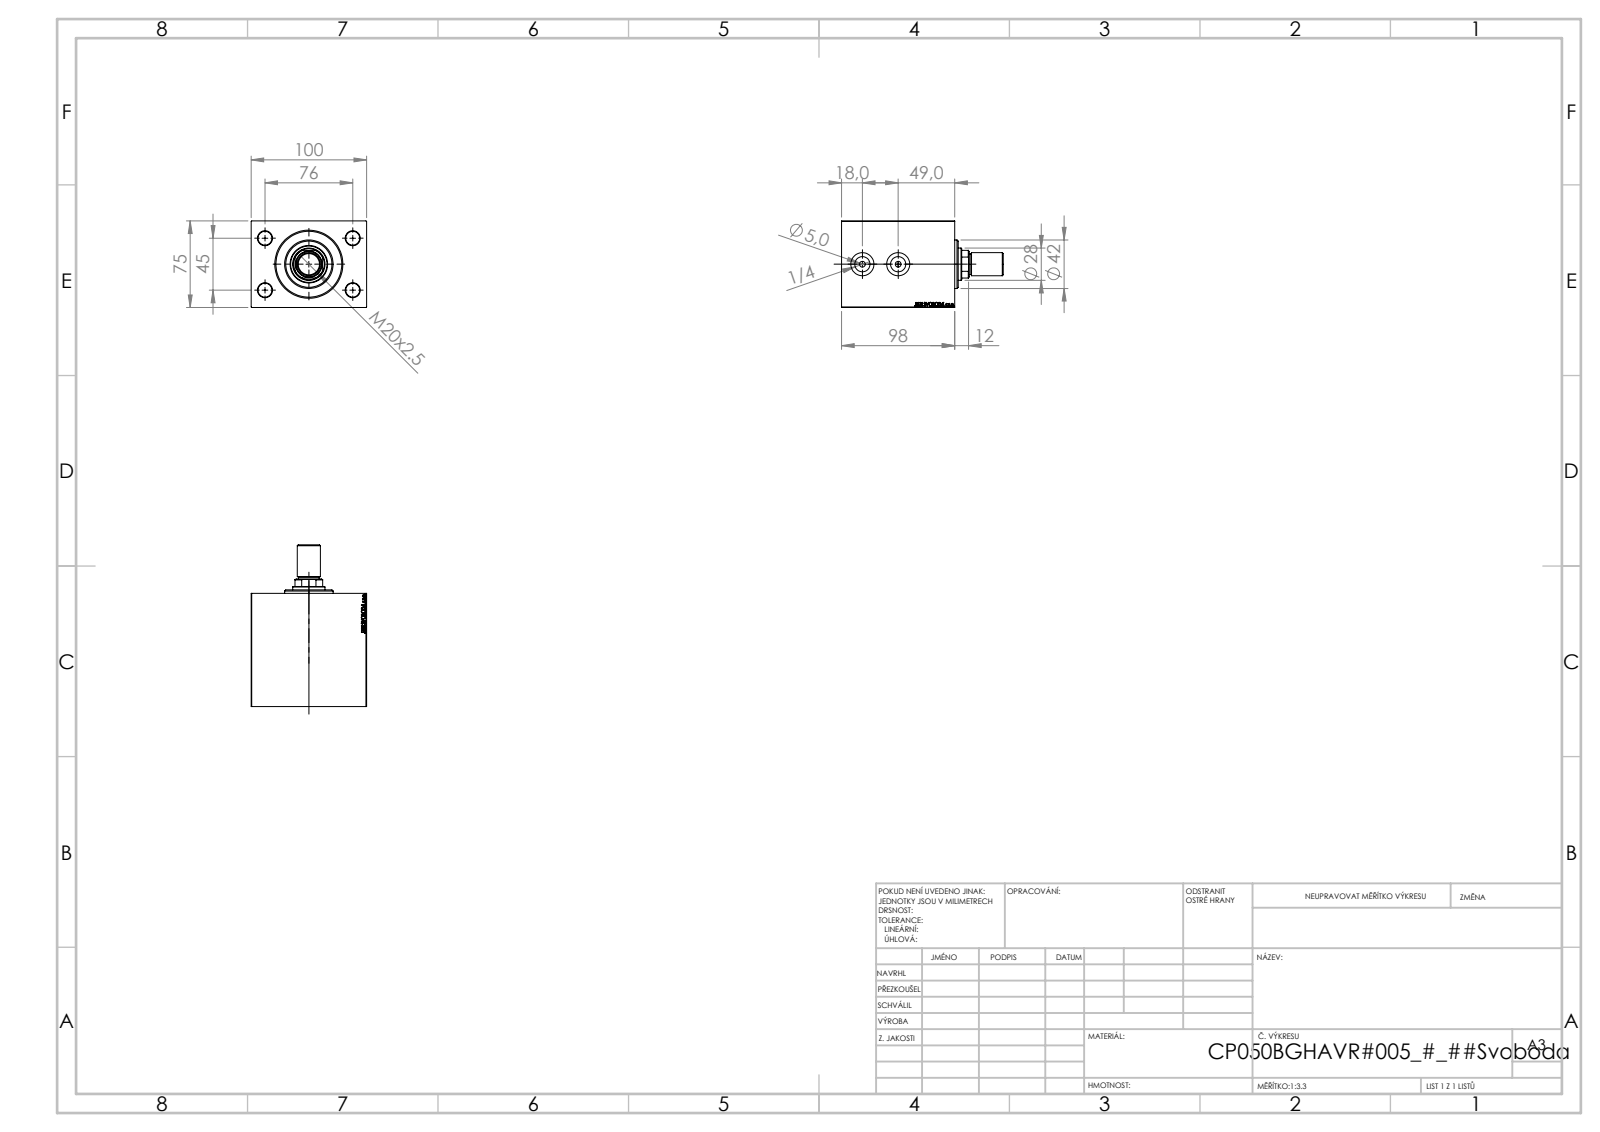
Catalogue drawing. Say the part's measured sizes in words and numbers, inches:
The part is named "V450CP_VC_B; V450CP_B; V450CP_B_VCP; V450CM_MALE_METRIC". Its 3-D file was written by "SolidWorks 2019 (CONFIG_CONTROL_DESIGN)". It is 4 solids with 918 faces: 410 planar, 72 cylindrical and 436 other. Overall it measures 5.512 by 3.937 by 2.953 inches. Its volume is 43.59 cubic inches and its surface area 164.8 square inches. Round holes: 4 of diameter 0.472, 2 of diameter 0.157, 2 of diameter 0.197, 2 of diameter 0.383, 2 of diameter 0.518, 2 of diameter 0.591, 2 of diameter 0.787, 1 of diameter 0.728, 1 of diameter 1.102, 1 of diameter 1.24, 1 of diameter 1.28, 1 of diameter 1.969. Round bosses or shafts: 1 of diameter 1.654, 1 of diameter 0.787, 1 of diameter 0.709. Partial cylindrical surfaces (rounded edges, fillets, slot ends): 1 of radius 0.531. The main face-to-face distances are 2.953, 3.937, 3.858, 1.929, 0.551, 3.307, 1.732, 0.197, 1.378, 1.181. The hole center spacings are 1.739, 1.772, 2.992, 3.477, 1.22, 1.675.
